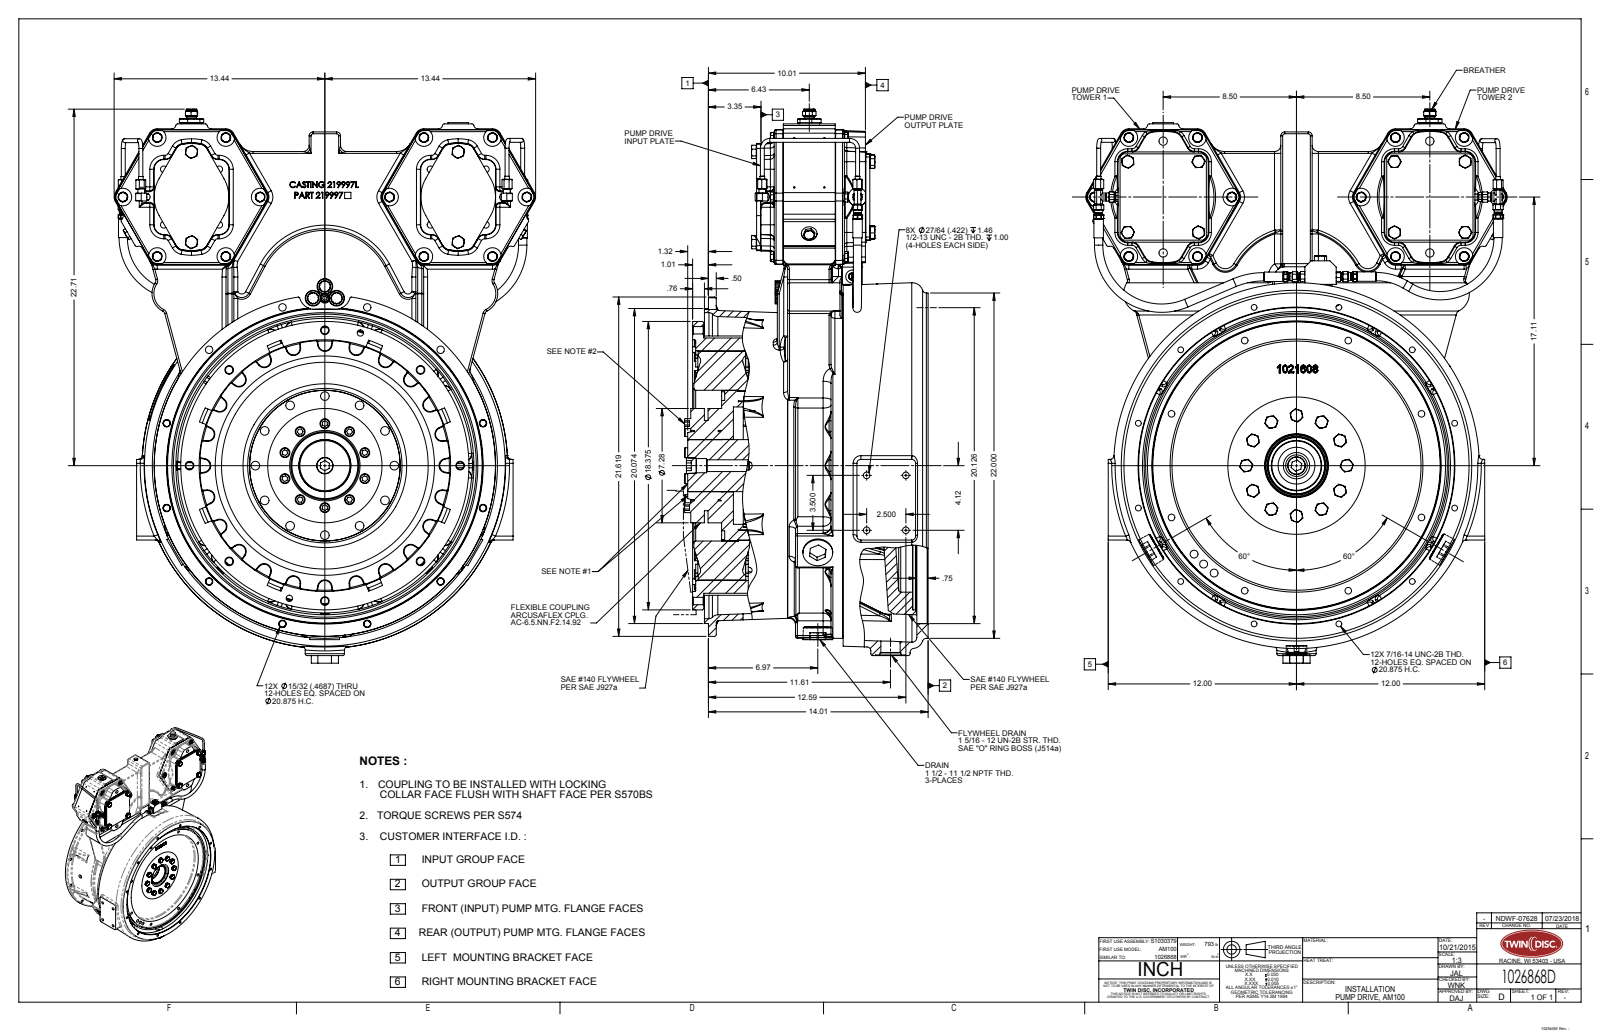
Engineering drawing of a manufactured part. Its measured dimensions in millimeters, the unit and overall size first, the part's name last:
Units: millimetres
Overall size (bounding box): 896.54 × 682.5 × 394.34
Round holes (diameter × count): ⌀10.72 ×20, ⌀12 ×20, ⌀9.35 ×12, ⌀11.11 ×8, ⌀14 ×8, ⌀13.49 ×4, ⌀14.68 ×4, ⌀2.71 ×3, ⌀12.7 ×3, ⌀10.2 ×2, ⌀15.87 ×2, ⌀25.4 ×2
Round bosses / shafts (diameter × count): ⌀15.75 ×21, ⌀18.87 ×18, ⌀14.14 ×15, ⌀16 ×10, ⌀11.11 ×6, ⌀6.35 ×6, ⌀15.27 ×4, ⌀13.46 ×4
Partial cylindrical surfaces — rounded edges, fillets, slot ends (radius × count): R3.05 ×91, R6.35 ×83, R12.7 ×62, R2.54 ×46, R10.67 ×24, R14.22 ×18, R4.06 ×16, R11.67 ×15
Main face-to-face distances: 106.56, 89.89, 16.67, 218.14, 19.69, 70.2, 86.87, 12.7, 36.04, 55.73
Hole centre spacings: 265.11, 512.16, 265.12, 374.93, 459.19, 458.73, 55.8, 374.92
Bodies: 0 solids, 3447 faces (1250 planar, 1019 cylindrical, 1178 other)
Part name (STEP PRODUCT): 1026868D
STEP written by: SolidWorks 2015 (AUTOMOTIVE_DESIGN)
